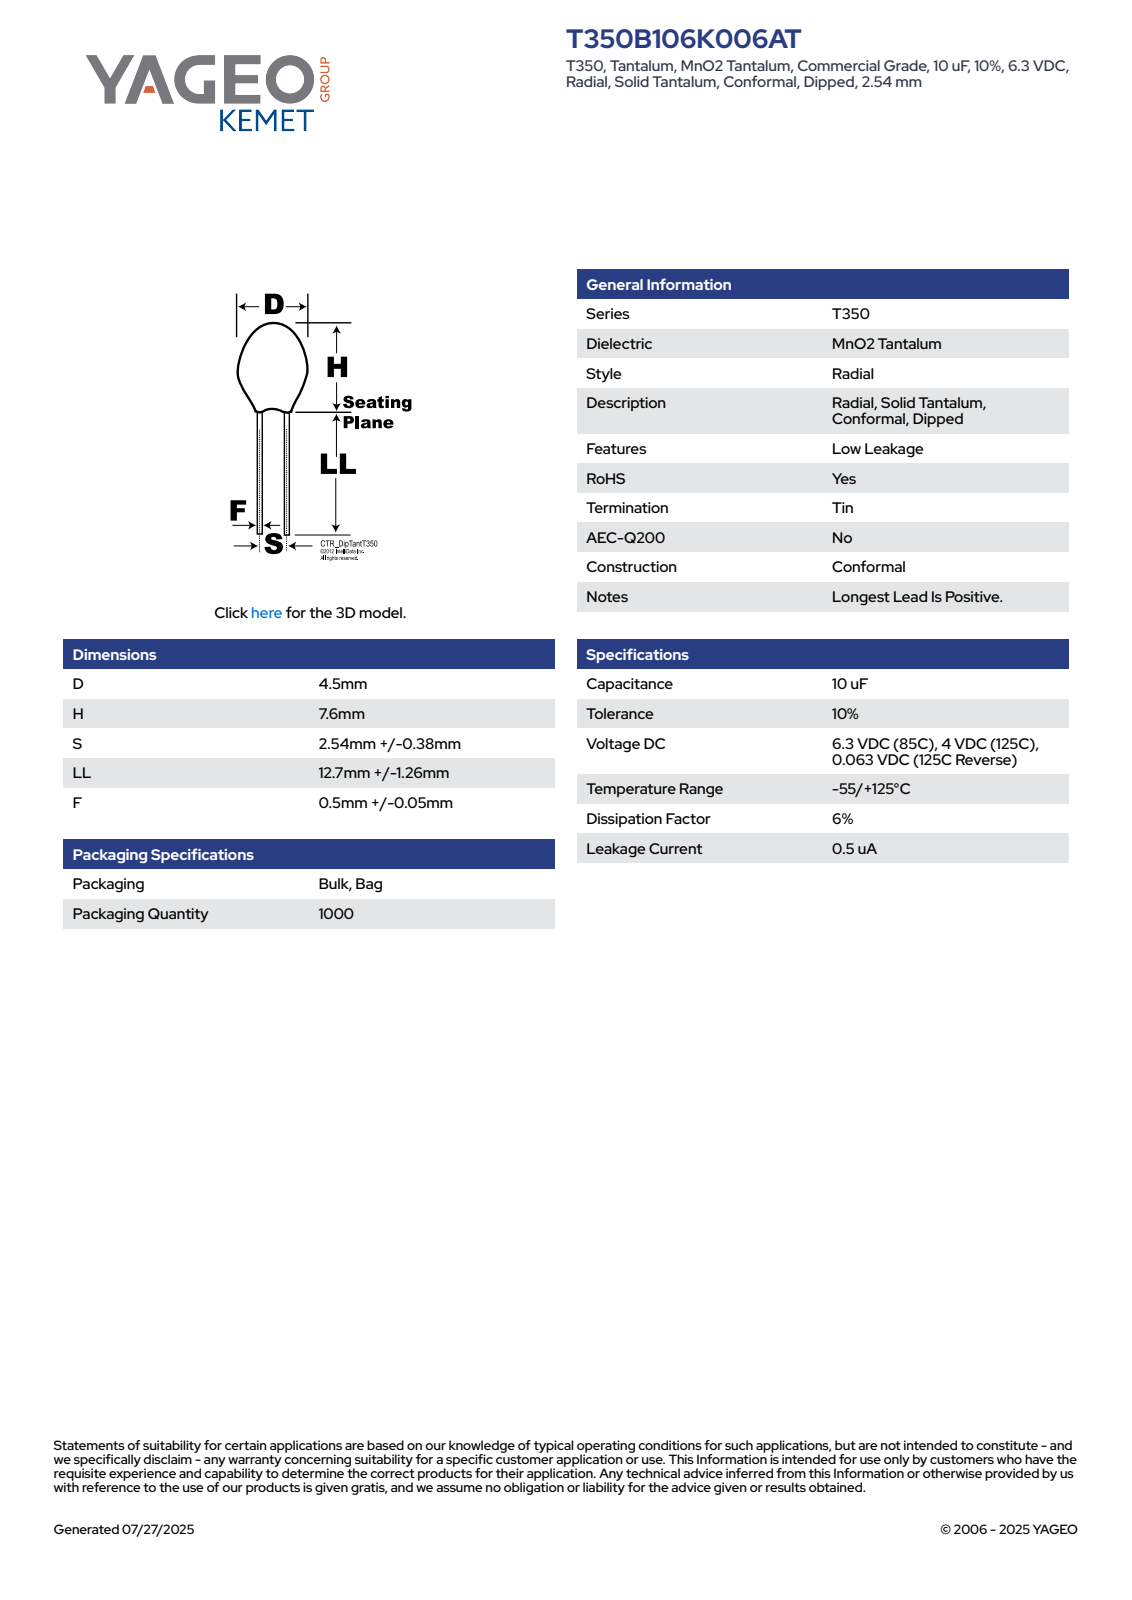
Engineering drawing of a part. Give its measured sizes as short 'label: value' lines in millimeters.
name: CTR_T350_D4.5H7.6S2.54LL13.96F0.55
written by: SolidWorks 2014 (AUTOMOTIVE_DESIGN)
unit: mm
bodies: 1 solid, 73 faces (26 planar, 10 cylindrical, 37 other)
size: 21.56 × 4.5 × 4.5
volume: 110 mm³; area: 164 mm²
bosses: 2× ⌀0.55, 1× ⌀4.5
rounds: 1× R2.24
face distances: 7.6, 13.96, 21.56, 18.15, 4.19, 3.41, 17.42, 3.46, 0.73, 4.14
